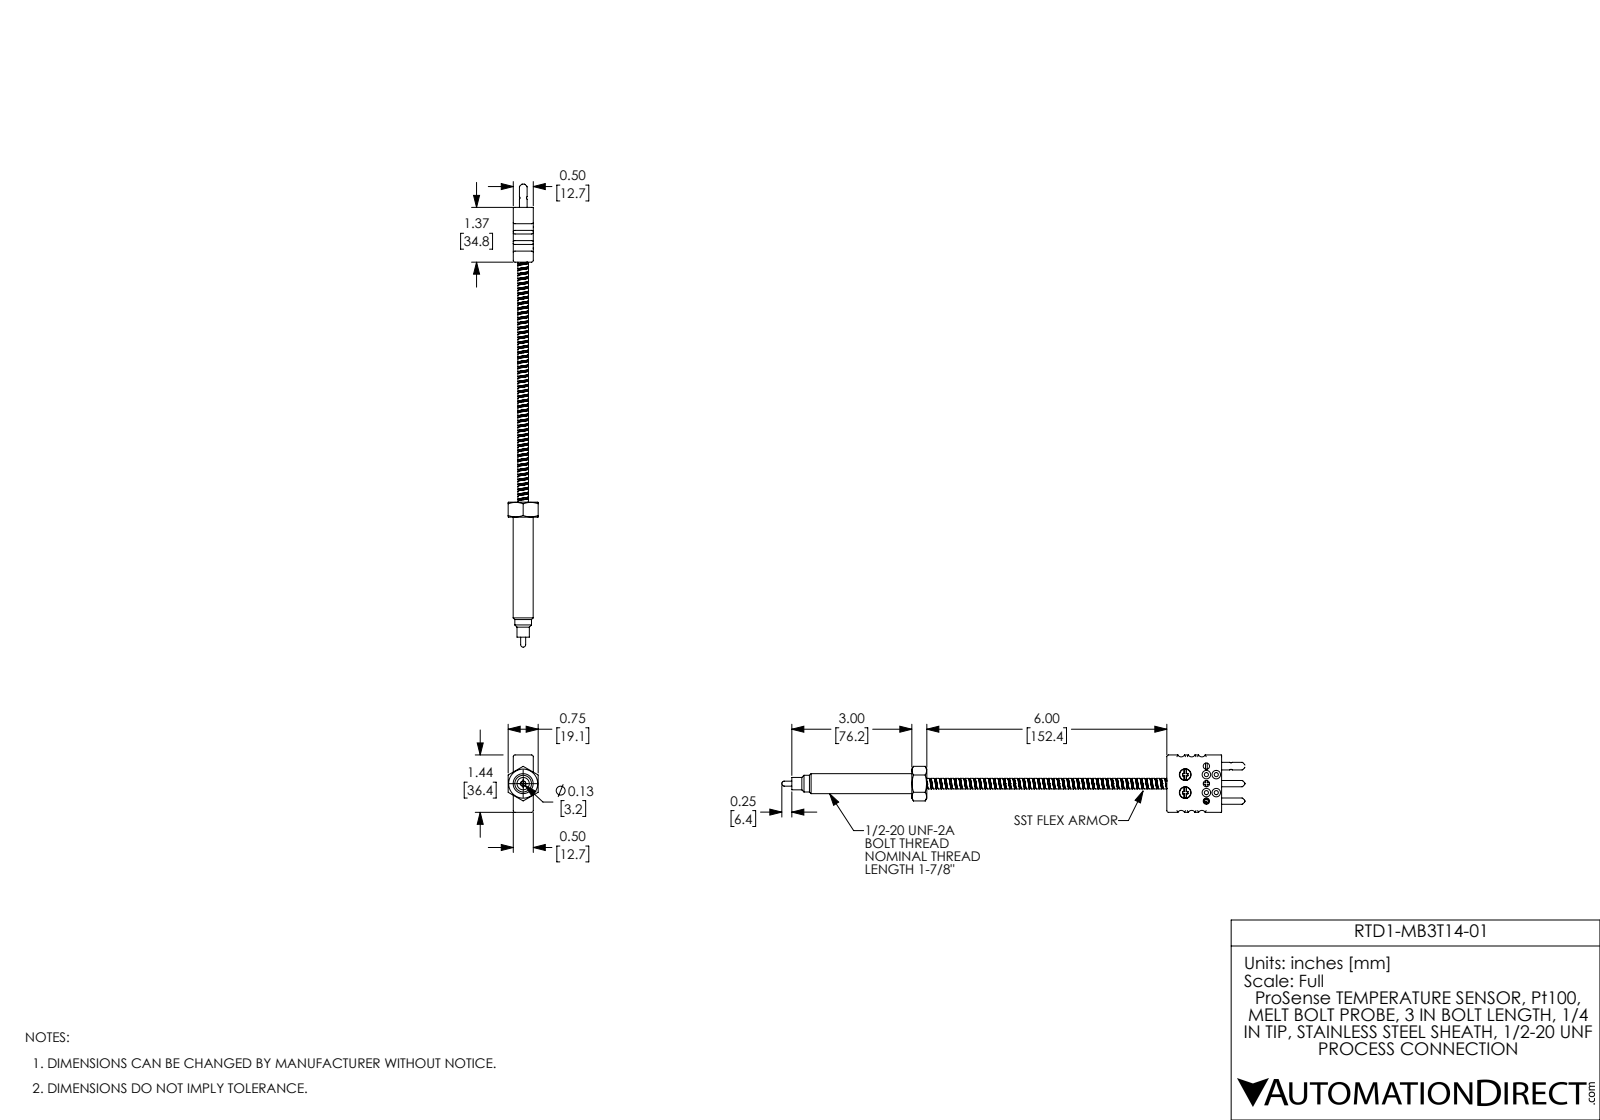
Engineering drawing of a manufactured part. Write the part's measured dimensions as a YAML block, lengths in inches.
part_name: "RTD1-MB3T14-01"
step_written_by: "SolidWorks 2017 (AUTOMOTIVE_DESIGN)"
units: inches
bodies: {solids: 3, faces: 414, planar: 106, cylindrical: 190, other: 118}
overall_size: [11.574, 1.435, 0.75]
volume: 1.981
surface_area: 21.84
round_holes:
  - {diameter: 0.103, count: 4}
  - {diameter: 0.158, count: 3}
  - {diameter: 0.185, count: 2}
  - {diameter: 0.294, count: 2}
  - {diameter: 0.135, count: 1}
  - {diameter: 0.308, count: 1}
round_bosses_or_shafts:
  - {diameter: 0.278, count: 2}
  - {diameter: 0.156, count: 2}
  - {diameter: 0.102, count: 2}
  - {diameter: 0.5, count: 1}
  - {diameter: 0.417, count: 1}
  - {diameter: 0.309, count: 1}
  - {diameter: 0.265, count: 1}
  - {diameter: 0.191, count: 1}
partial_cylinders:
  - {radius: 0.045, count: 8}
  - {radius: 0.095, count: 6}
  - {radius: 0.01, count: 4}
face_to_face_distances: [0.5, 1.369, 0.75, 7.369, 6, 1.435, 7.744, 6.375, 0.375, 0.622]
hole_center_spacings: [0.529, 0.57, 0.776, 0.212, 0.225, 0.247, 0.326, 0.334]
